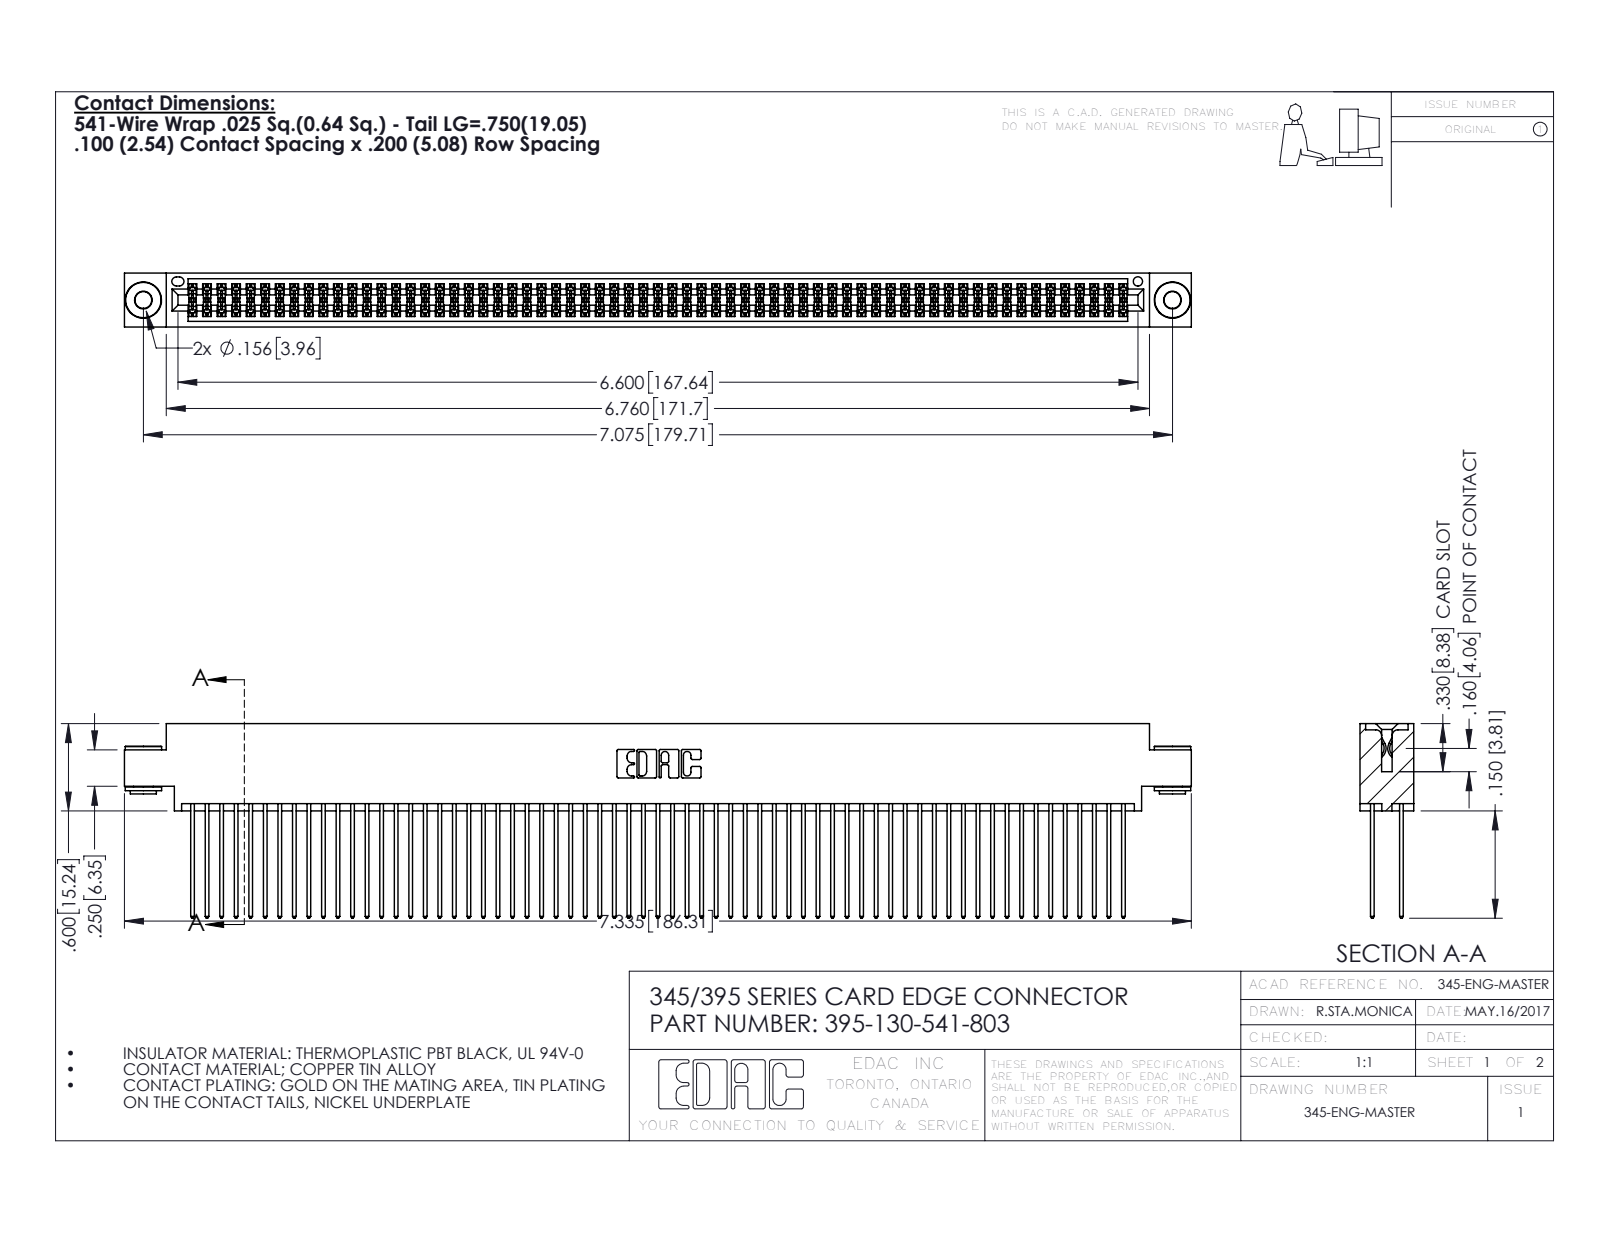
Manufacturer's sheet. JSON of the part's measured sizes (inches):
{"part_name": "395-130-541-803; 345 Part_0.170 Offset - 0.156 Dia-TH; 345-292-001_345-293-141; 345-250-002_345-250-002-102", "step_written_by": "SolidWorks 2016 (CONFIG_CONTROL_DESIGN)", "units": "inches", "bodies": {"solids": 133, "faces": 6668, "planar": 4384, "cylindrical": 2276, "other": 8}, "overall_size": [7.335, 1.337, 0.37], "volume_in3": 1.157, "surface_area_in2": 50.11, "round_holes": [[0.116, 2], [0.156, 2], [0.064, 1]], "round_bosses_or_shafts": [[0.25, 2], [0.18, 2], [0.136, 2]], "partial_cylinders_radius": [[0.006, 195], [0.01, 130], [0.01, 22], [0.007, 6], [0.031, 6], [0.026, 3], [0.014, 2], [0.019, 2]], "face_to_face_distances": [0.072, 0.298, 0.2, 0.098, 0.272, 0.025, 0.225, 0.37, 0.175, 0.149], "hole_center_spacings": [0.27, 6.839, 7.075]}
